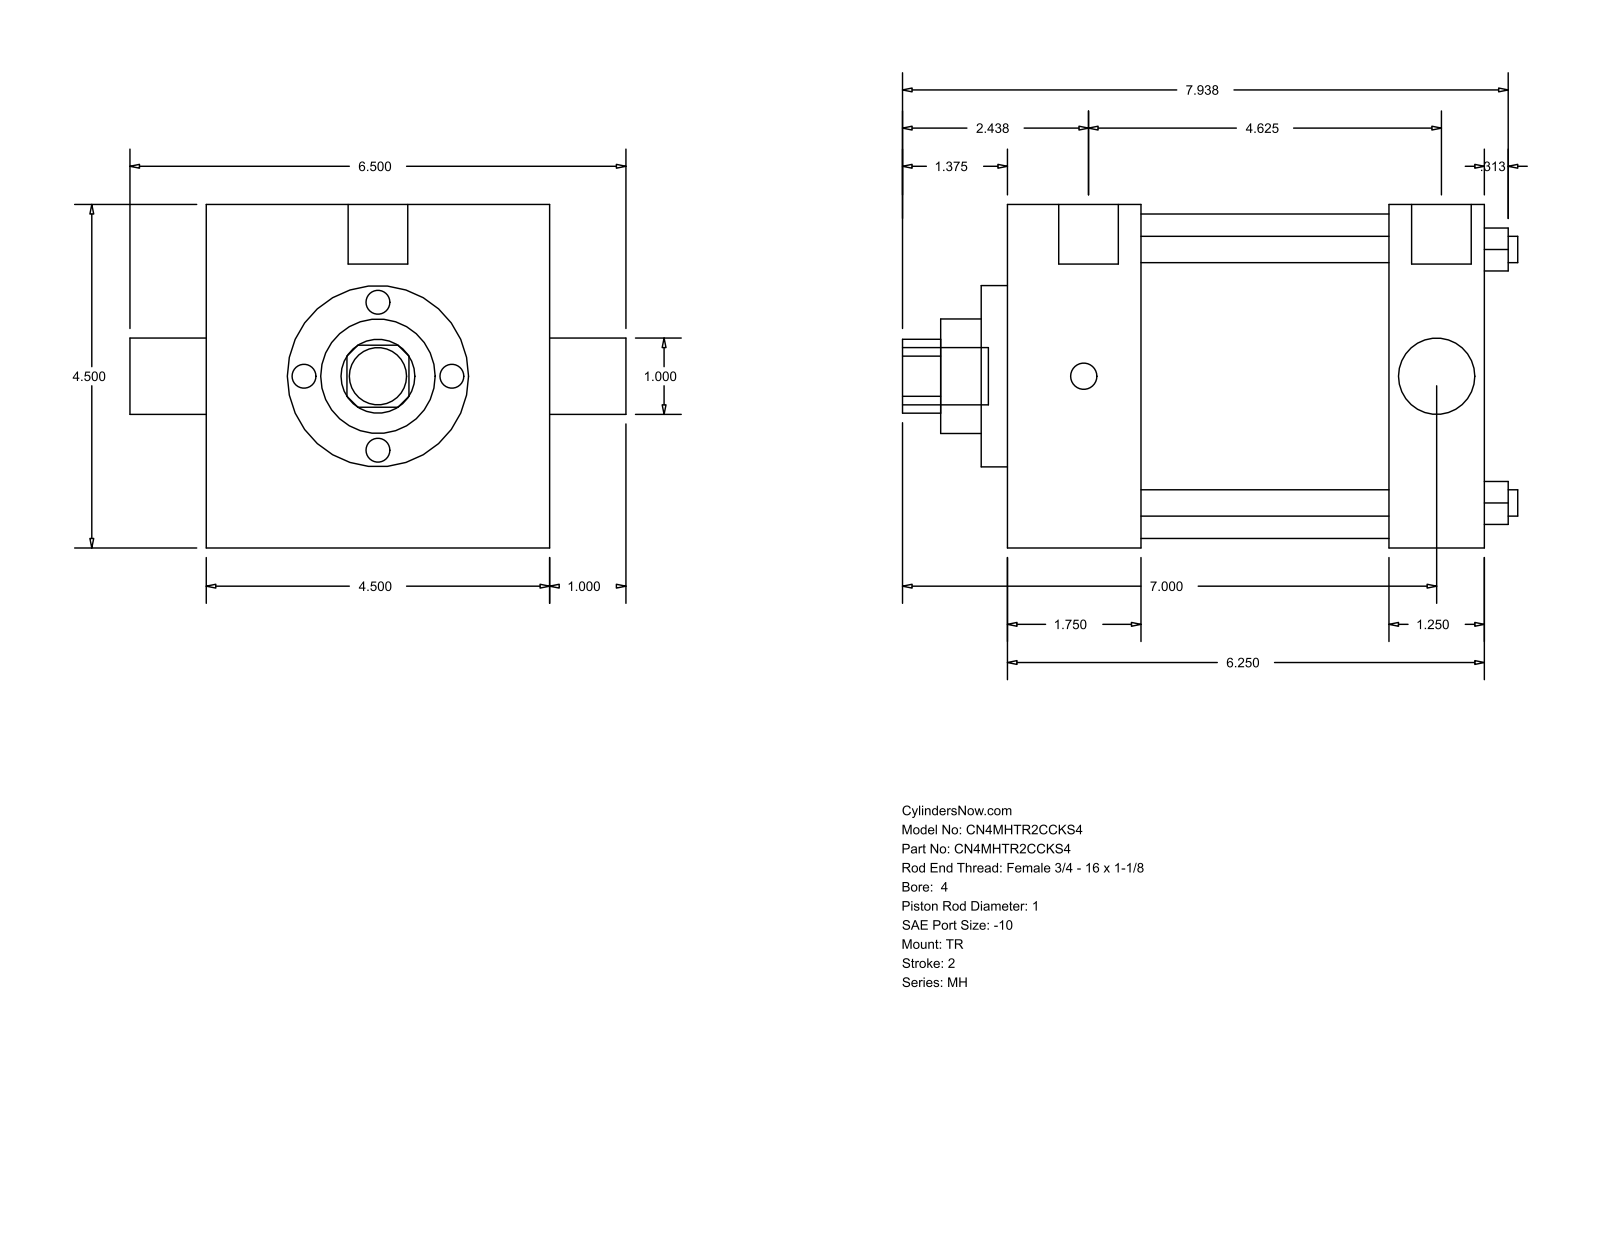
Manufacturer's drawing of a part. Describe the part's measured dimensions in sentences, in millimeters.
The part is named "MH_TR__0400_1". Its 3-D file was written by "GSSL Pune (CONFIG_CONTROL_DESIGN)". It is 0 solids with 86 faces: 61 planar, 25 cylindrical and 0 other. Overall it measures 204.79 by 165.1 by 114.3 millimeters. Round holes: 4 of diameter 8.76, 2 of diameter 25.4, 1 of diameter 38.1, 1 of diameter 60.33, 1 of diameter 107.95. Round bosses or shafts: 3 of diameter 8.73, 2 of diameter 19.84, 1 of diameter 19.05. Partial cylindrical surfaces (rounded edges, fillets, slot ends): 1 of radius 12.29. The main face-to-face distances are 114.3, 158.76, 44.46, 127.01, 82.55, 31.75, 8.73, 53.19, 135.74, 167.49. The hole center spacings are 59.62, 84.32, 119.25.
